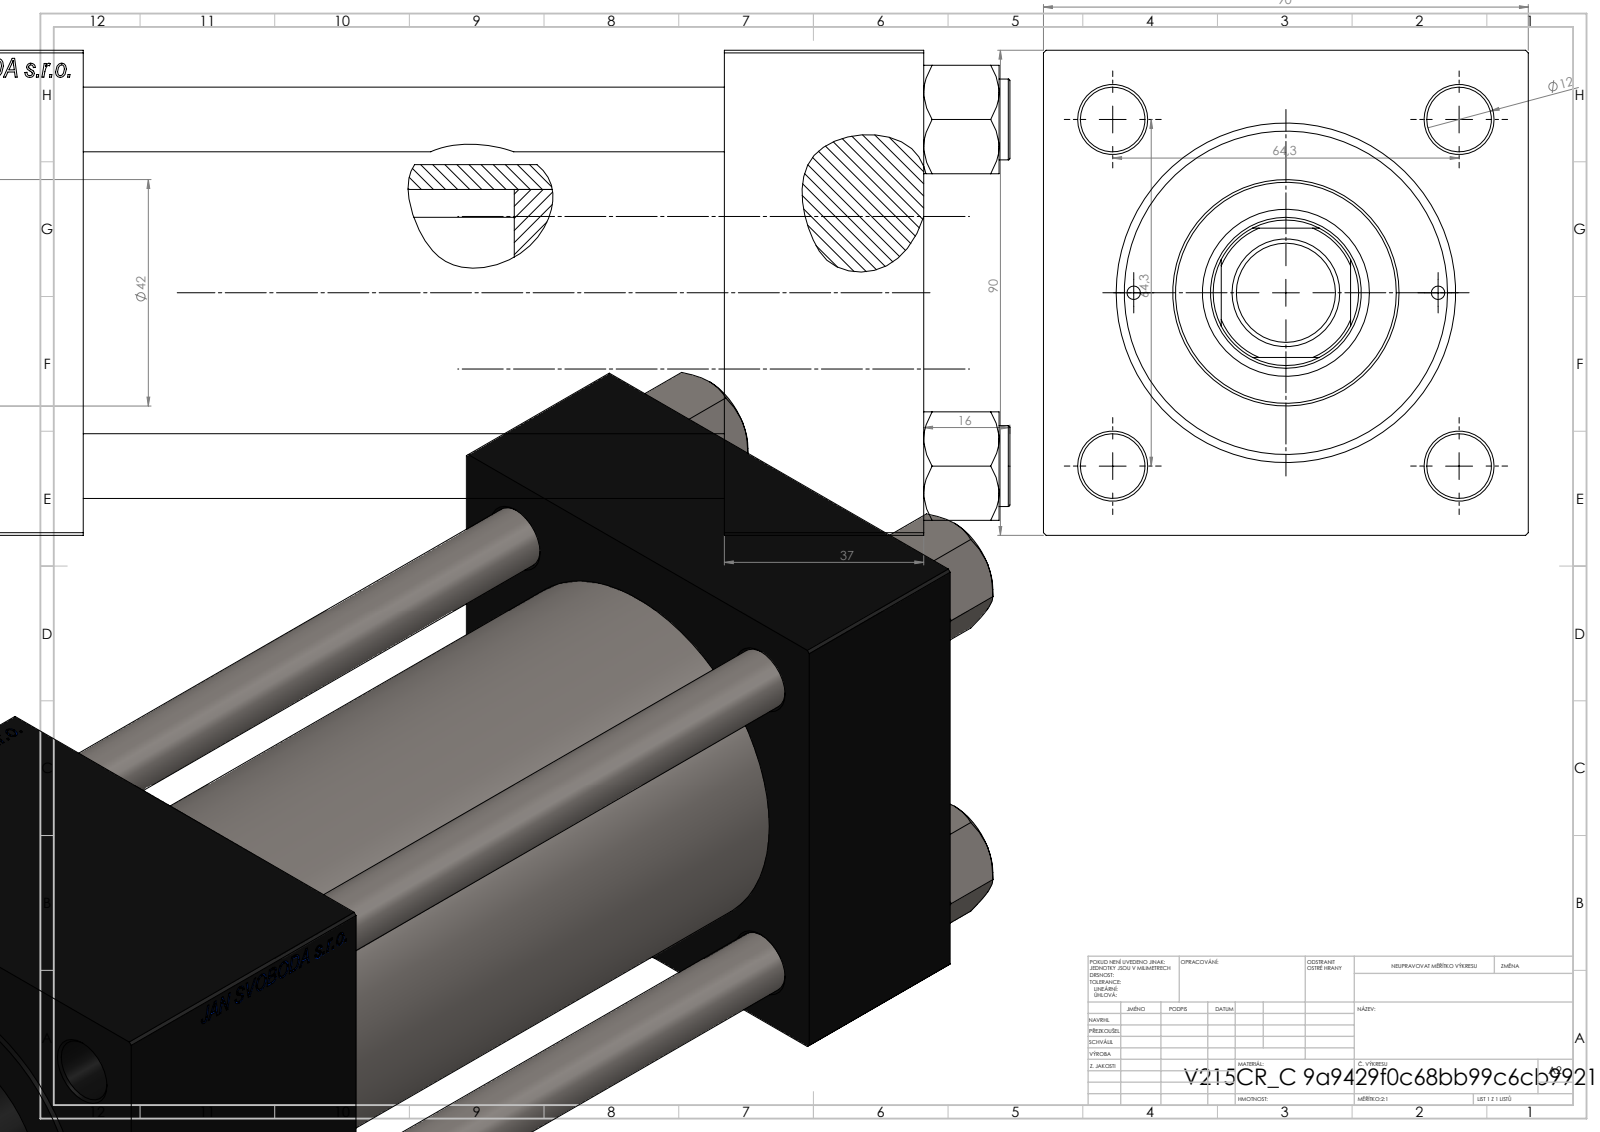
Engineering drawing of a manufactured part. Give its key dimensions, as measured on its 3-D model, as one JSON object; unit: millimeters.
{"part_name": "NUT_M5_C; ROD_END_AH; V215CR_VCP_C; V215CR_C_Body (+2 more)", "step_written_by": "SolidWorks 2019 (CONFIG_CONTROL_DESIGN)", "units": "millimeters", "bodies": {"solids": 12, "faces": 1168, "planar": 532, "cylindrical": 94, "other": 542}, "overall_size": [291, 90, 90], "volume_mm3": 1057000, "surface_area_mm2": 220847, "round_holes": [[12, 4], [2.5, 2], [7, 2], [20.96, 2], [30, 2], [18.5, 1], [28, 1], [31, 1], [50, 1], [60, 1], [63, 1]], "round_bosses_or_shafts": [[15, 4], [69, 1], [42, 1], [20, 1], [18, 1]], "partial_cylinders_radius": [[13.5, 1]], "face_to_face_distances": [90, 37, 215, 178, 119, 156, 59, 186.3, 149.3, 30.3], "hole_center_spacings": [32.39, 45.47, 64.3, 68.42, 28.25, 90.93, 56.5, 157.5]}
